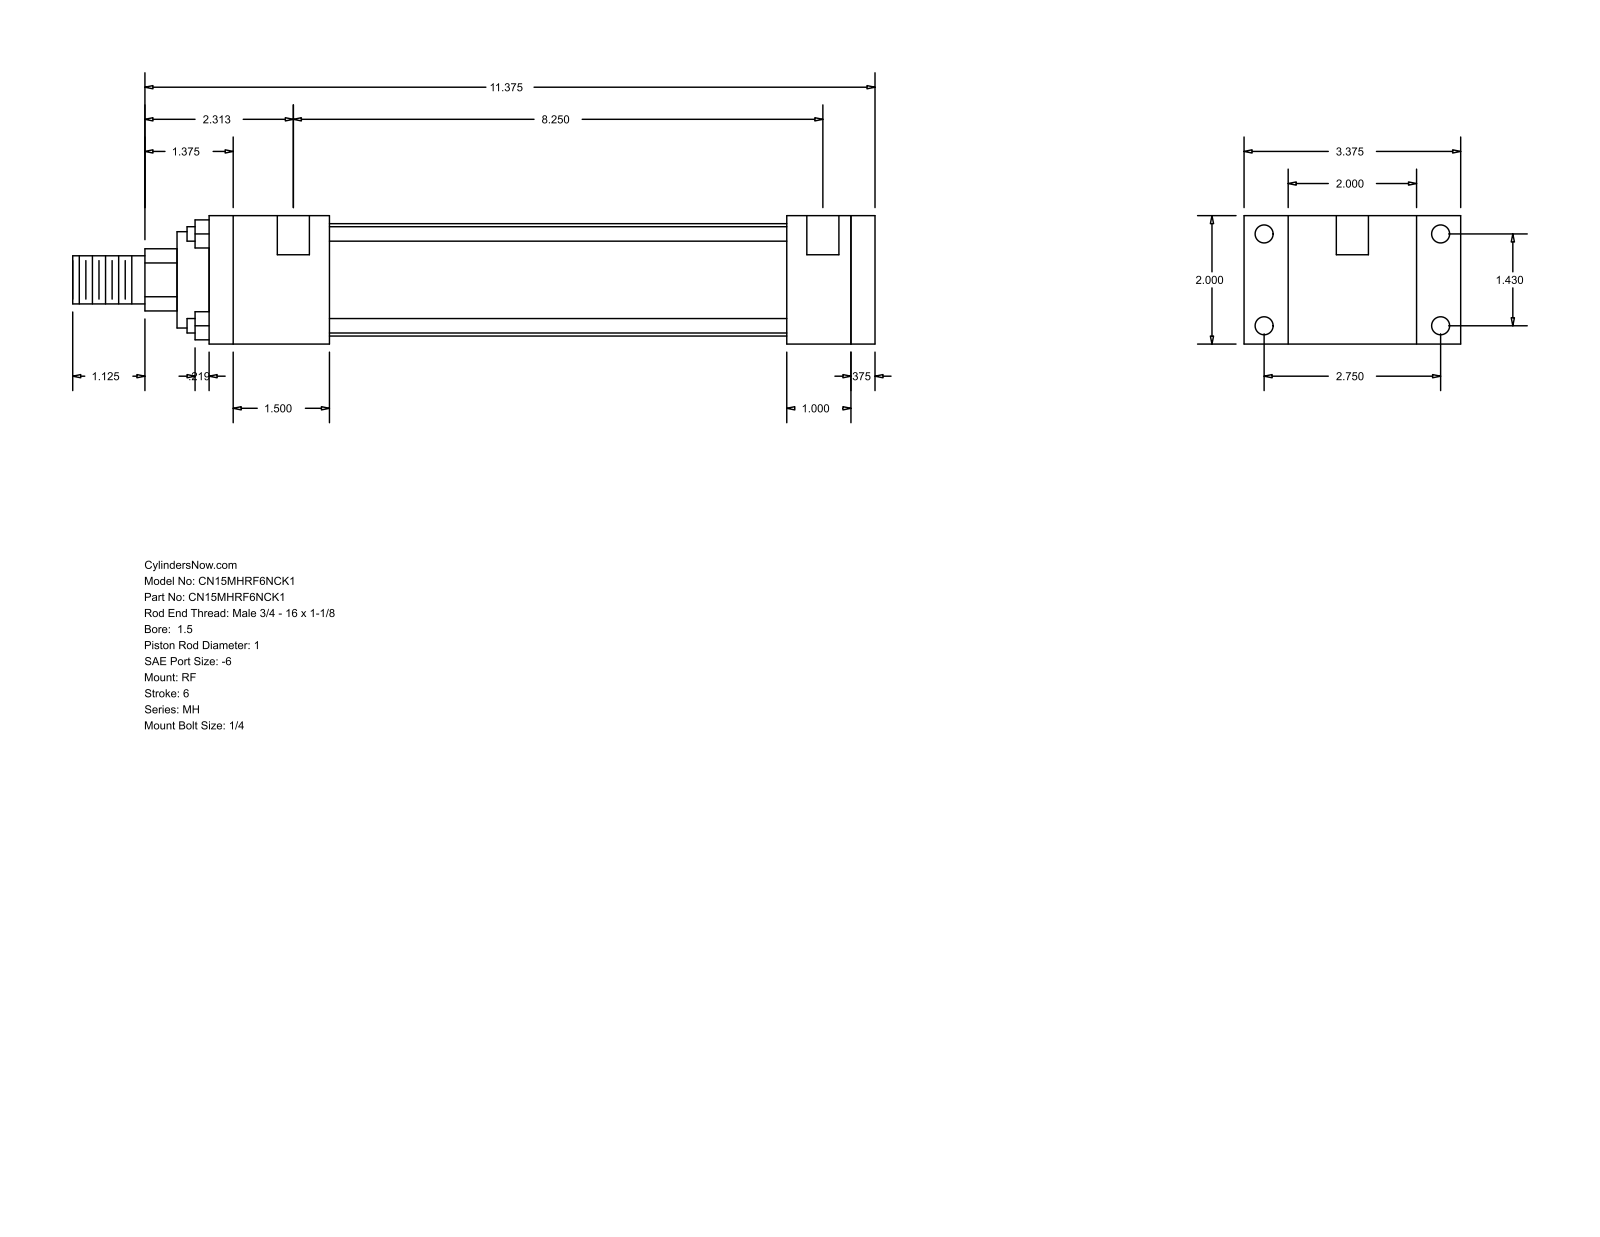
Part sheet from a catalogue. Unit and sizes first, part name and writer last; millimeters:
Units: millimetres
Overall size (bounding box): 317.5 × 85.72 × 50.8
Round holes (diameter × count): ⌀5.56 ×4, ⌀7.14 ×4, ⌀12.7 ×2
Round bosses / shafts (diameter × count): ⌀5.71 ×4, ⌀44.45 ×1, ⌀38.1 ×1, ⌀25.4 ×1, ⌀19.05 ×1
Partial cylindrical surfaces — rounded edges, fillets, slot ends (radius × count): R12.29 ×1
Main face-to-face distances: 50.8, 9.53, 254, 25.4, 263.53, 17.46, 68.26, 228.6, 34.93, 47.63
Hole centre spacings: 36.32, 69.84, 78.72, 212.73, 3.18, 209.55
Bodies: 0 solids, 92 faces (64 planar, 28 cylindrical, 0 other)
Part name (STEP PRODUCT): MH_RF__0150_1
STEP written by: GSSL Pune (CONFIG_CONTROL_DESIGN)
